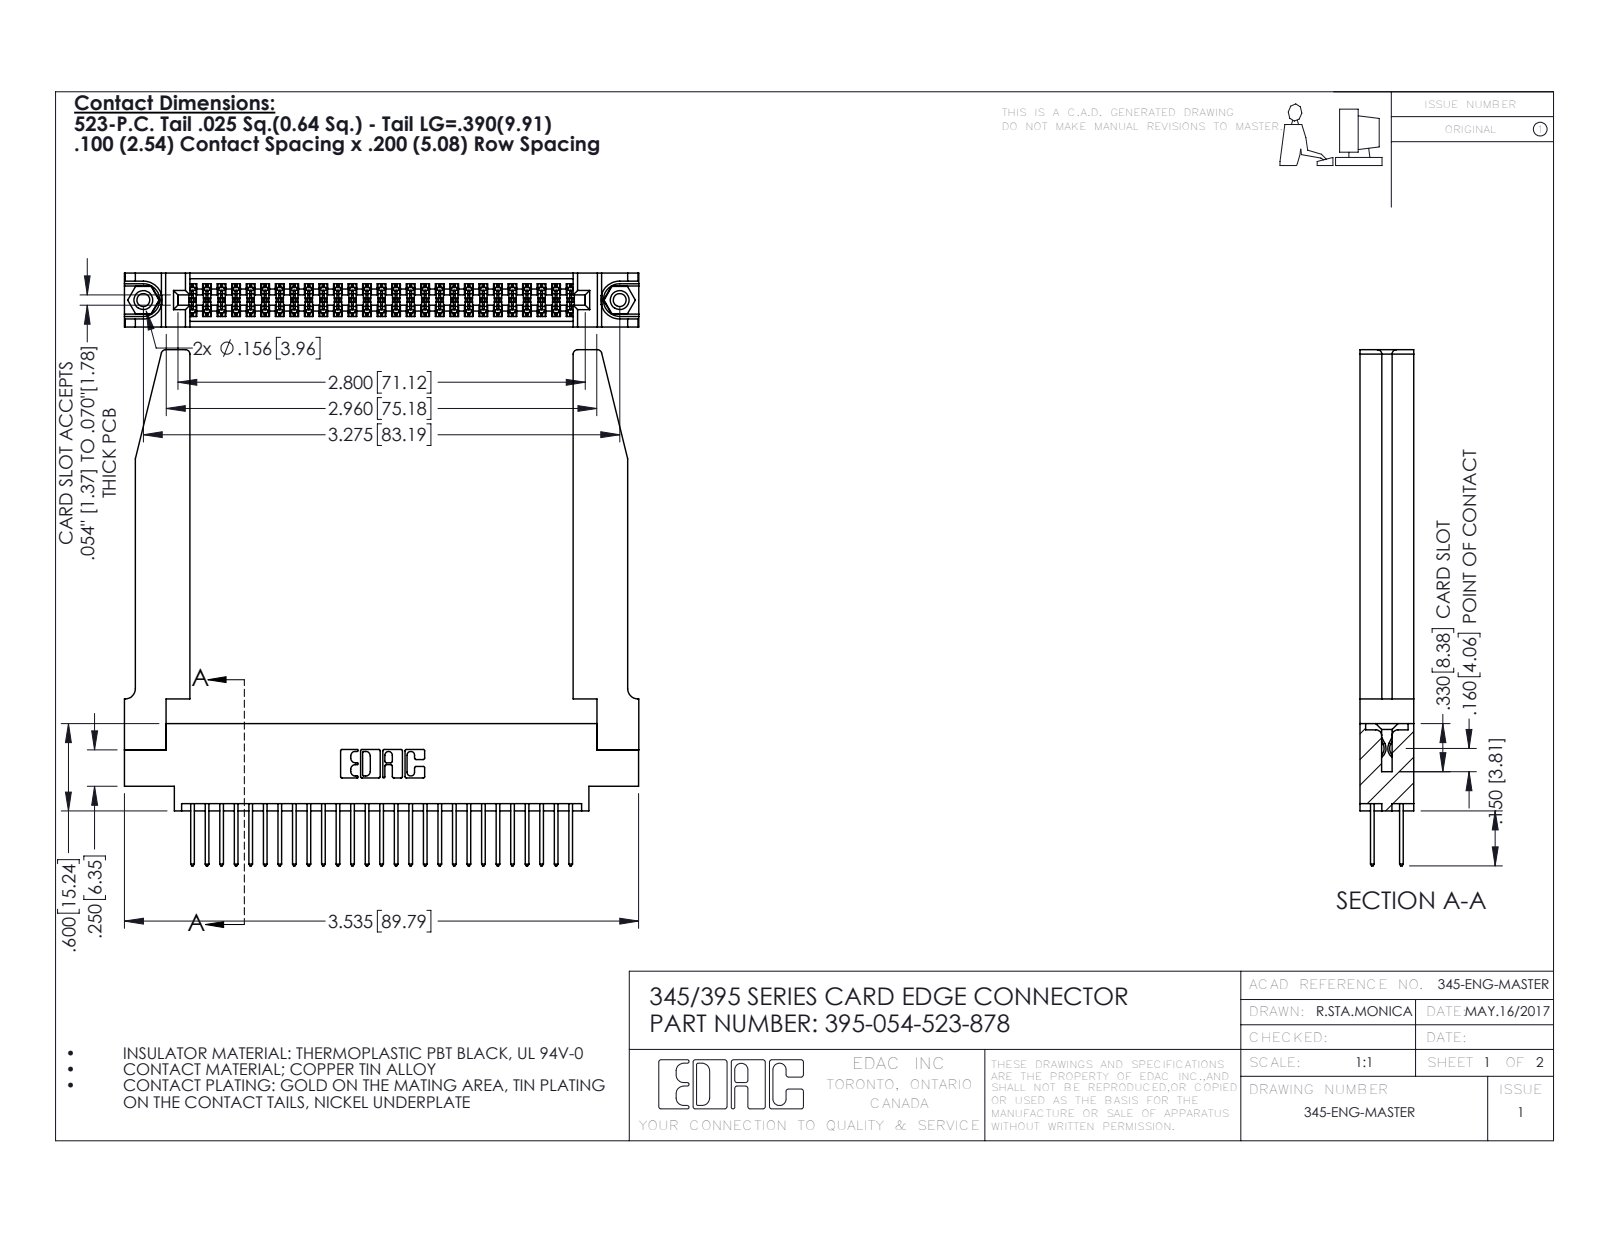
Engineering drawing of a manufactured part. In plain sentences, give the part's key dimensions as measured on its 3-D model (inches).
The part is named "345-250-001_345-250-001-102; 345-292-001_345-293-123; 395-054-523-878; 345-220-078_345-220-078 (+1 more)". Its 3-D file was written by "SolidWorks 2016 (CONFIG_CONTROL_DESIGN)". It is 59 solids with 3064 faces: 2008 planar, 1004 cylindrical and 52 other. Overall it measures 3.547 by 3.536 by 0.37 inches. Its volume is 0.998 cubic inches and its surface area 30.81 square inches. Round holes: 2 of diameter 0.089, 2 of diameter 0.125, 2 of diameter 0.156, 1 of diameter 0.064. Round bosses or shafts: 2 of diameter 0.155. Partial cylindrical surfaces (rounded edges, fillets, slot ends): 81 of radius 0.006, 54 of radius 0.01, 22 of radius 0.01, 8 of radius 0.03, 6 of radius 0.007, 6 of radius 0.031, 3 of radius 0.026, 2 of radius 0.014. The main face-to-face distances are 0.37, 0.072, 0.298, 0.098, 0.272, 0.025, 0.2, 0.225, 0.175, 0.148. The hole center spacings are 0.27, 3.04, 3.275.
